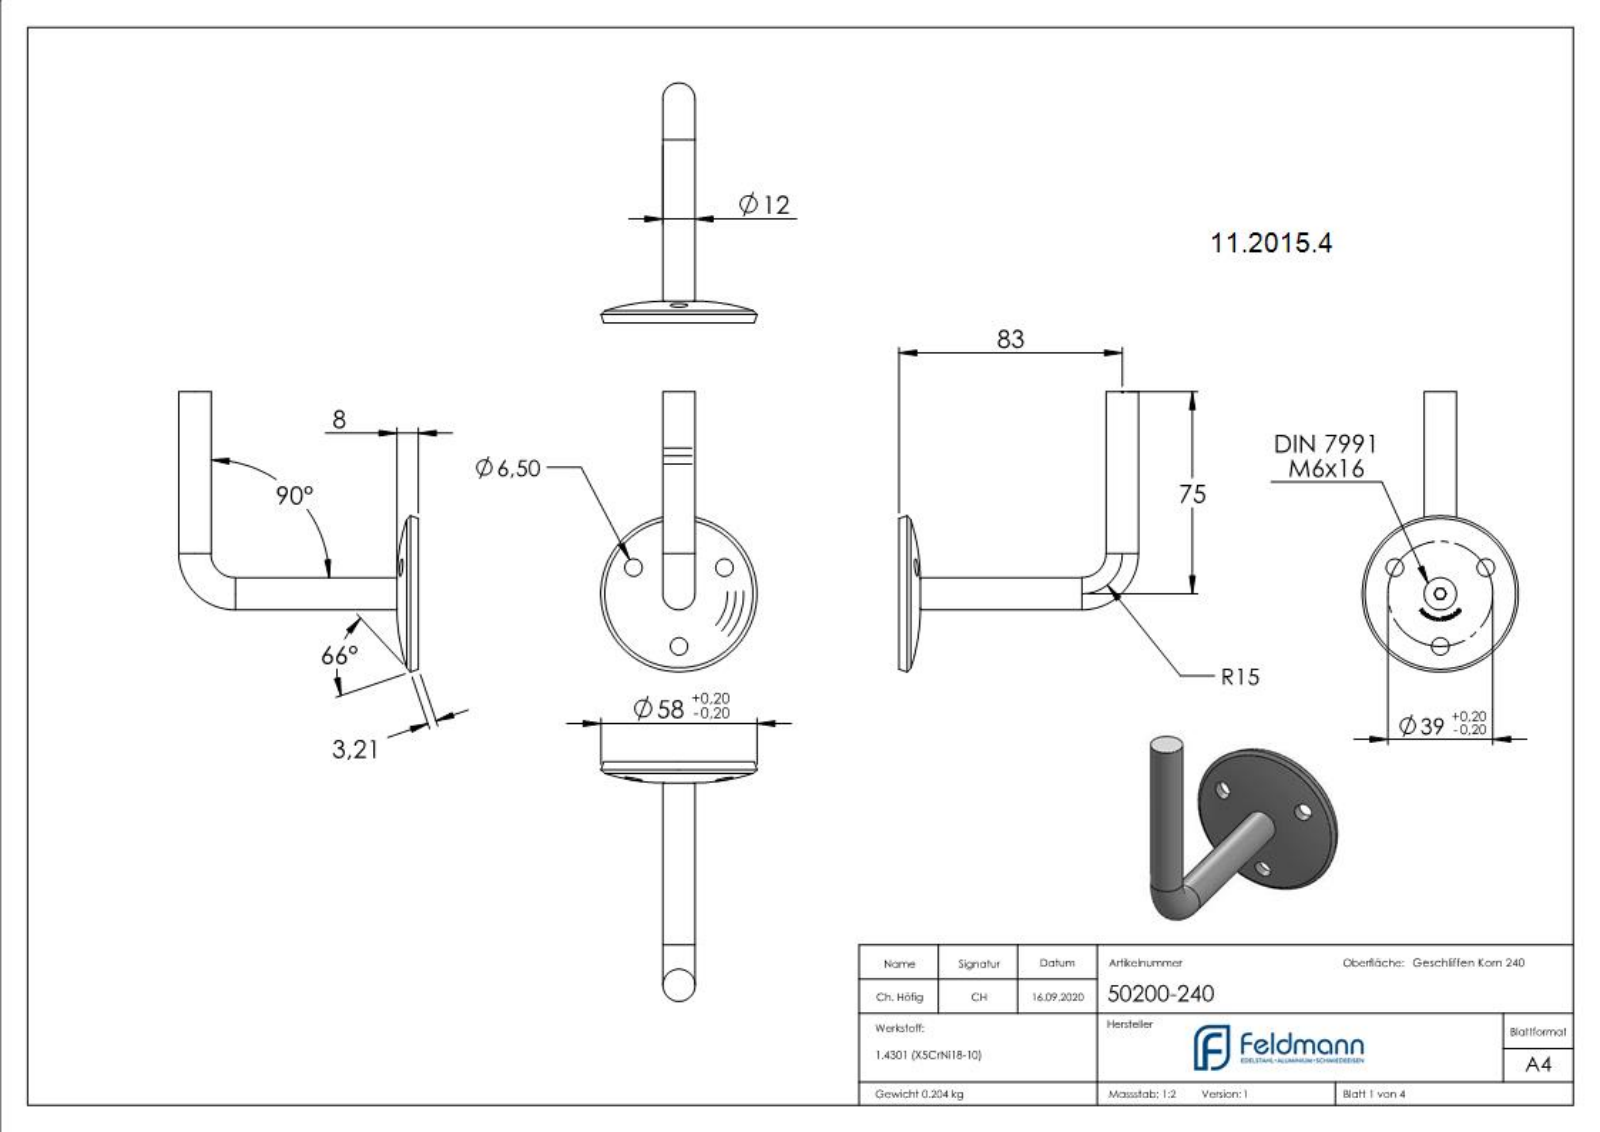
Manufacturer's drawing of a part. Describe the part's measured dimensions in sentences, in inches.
The part is named "50200-240 Teil1; 50200-240 Teil1_50200-240 Teil1; DIN-7991 M3-M10_DIN7991 M6x16; 50200-240 Teil2_50200-240 Teil2 (+3 more)". Its 3-D file was written by "SolidWorks 2018 (CONFIG_CONTROL_DESIGN)". It is 3 solids with 274 faces: 105 planar, 18 cylindrical and 151 other. Overall it measures 4.094 by 3.504 by 2.283 inches. Its volume is 1.577 cubic inches and its surface area 19.13 square inches. Round holes: 3 of diameter 0.256, 1 of diameter 0.197, 1 of diameter 0.413. Round bosses or shafts: 2 of diameter 0.472, 1 of diameter 0.236. The main face-to-face distances are 0.189, 0.157, 0.472, 0.283, 3.031, 2.874, 0.118, 0.071, 0.354, 0.021. The hole center spacings are 0.768, 1.33.
